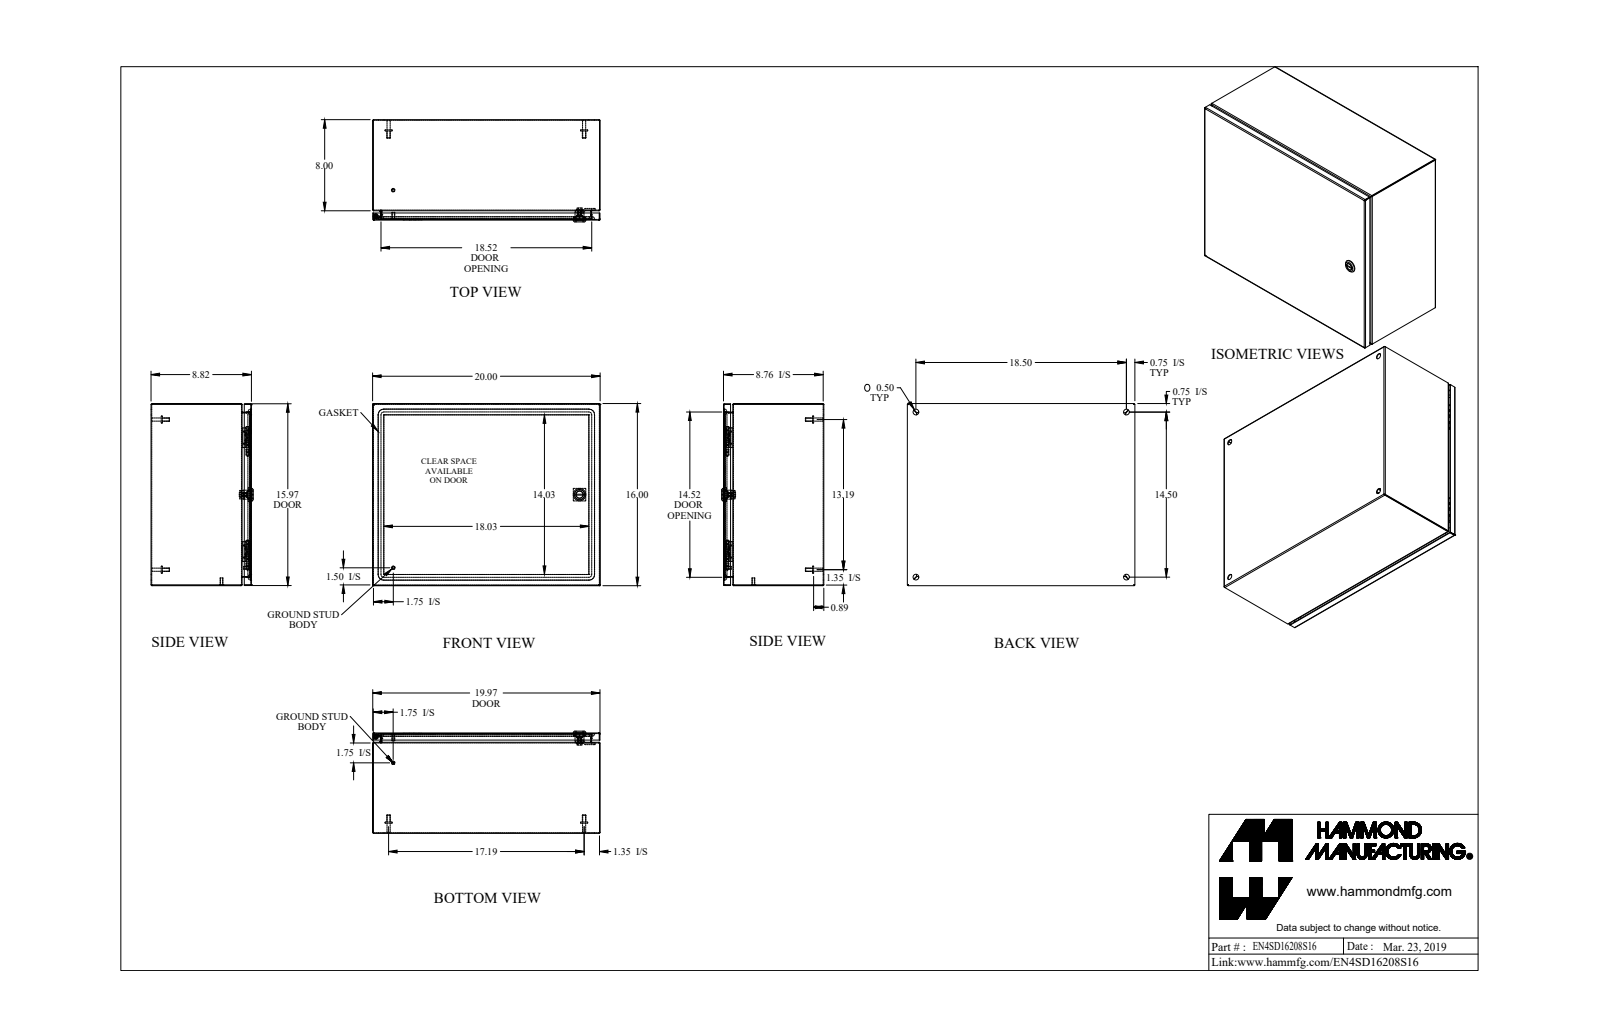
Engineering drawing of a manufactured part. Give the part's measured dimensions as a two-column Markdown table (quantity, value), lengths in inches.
| quantity | value |
| --- | --- |
| part name | EN4SD16208S16_Default |
| STEP written by | SolidWorks 2019 (CONFIG_CONTROL_DESIGN) |
| units | inches |
| bodies | 22 solids, 656 faces (303 planar, 211 cylindrical, 142 other) |
| overall size | 20 × 16 × 8.981 |
| volume | 84.46 in³ |
| surface area | 2 876 in² |
| round holes (diameter × count) | 0.5 × 5, 0.172 × 1, 0.197 × 1, 0.24 × 1, 0.242 × 1, 0.387 × 1, 0.63 × 1, 0.768 × 1 |
| round bosses / shafts (diameter × count) | 0.313 × 6, 0.625 × 5, 0.275 × 4, 0.25 × 2, 1.1 × 1, 0.785 × 1, 0.525 × 1, 0.475 × 1 |
| partial cylindrical surfaces (radius × count) | 0.029 × 21, 0.086 × 21, 0.188 × 12, 0.006 × 4, 0.062 × 4, 0.25 × 4, 0.499 × 4, 0.125 × 2 |
| main face-to-face distances | 0.057, 0.057, 8.707, 8.764, 8.764, 8.821, 15.943, 19.943, 15.886, 16 |
| hole center spacings | 7.327, 14.5, 18.5, 18.888, 23.506 |
